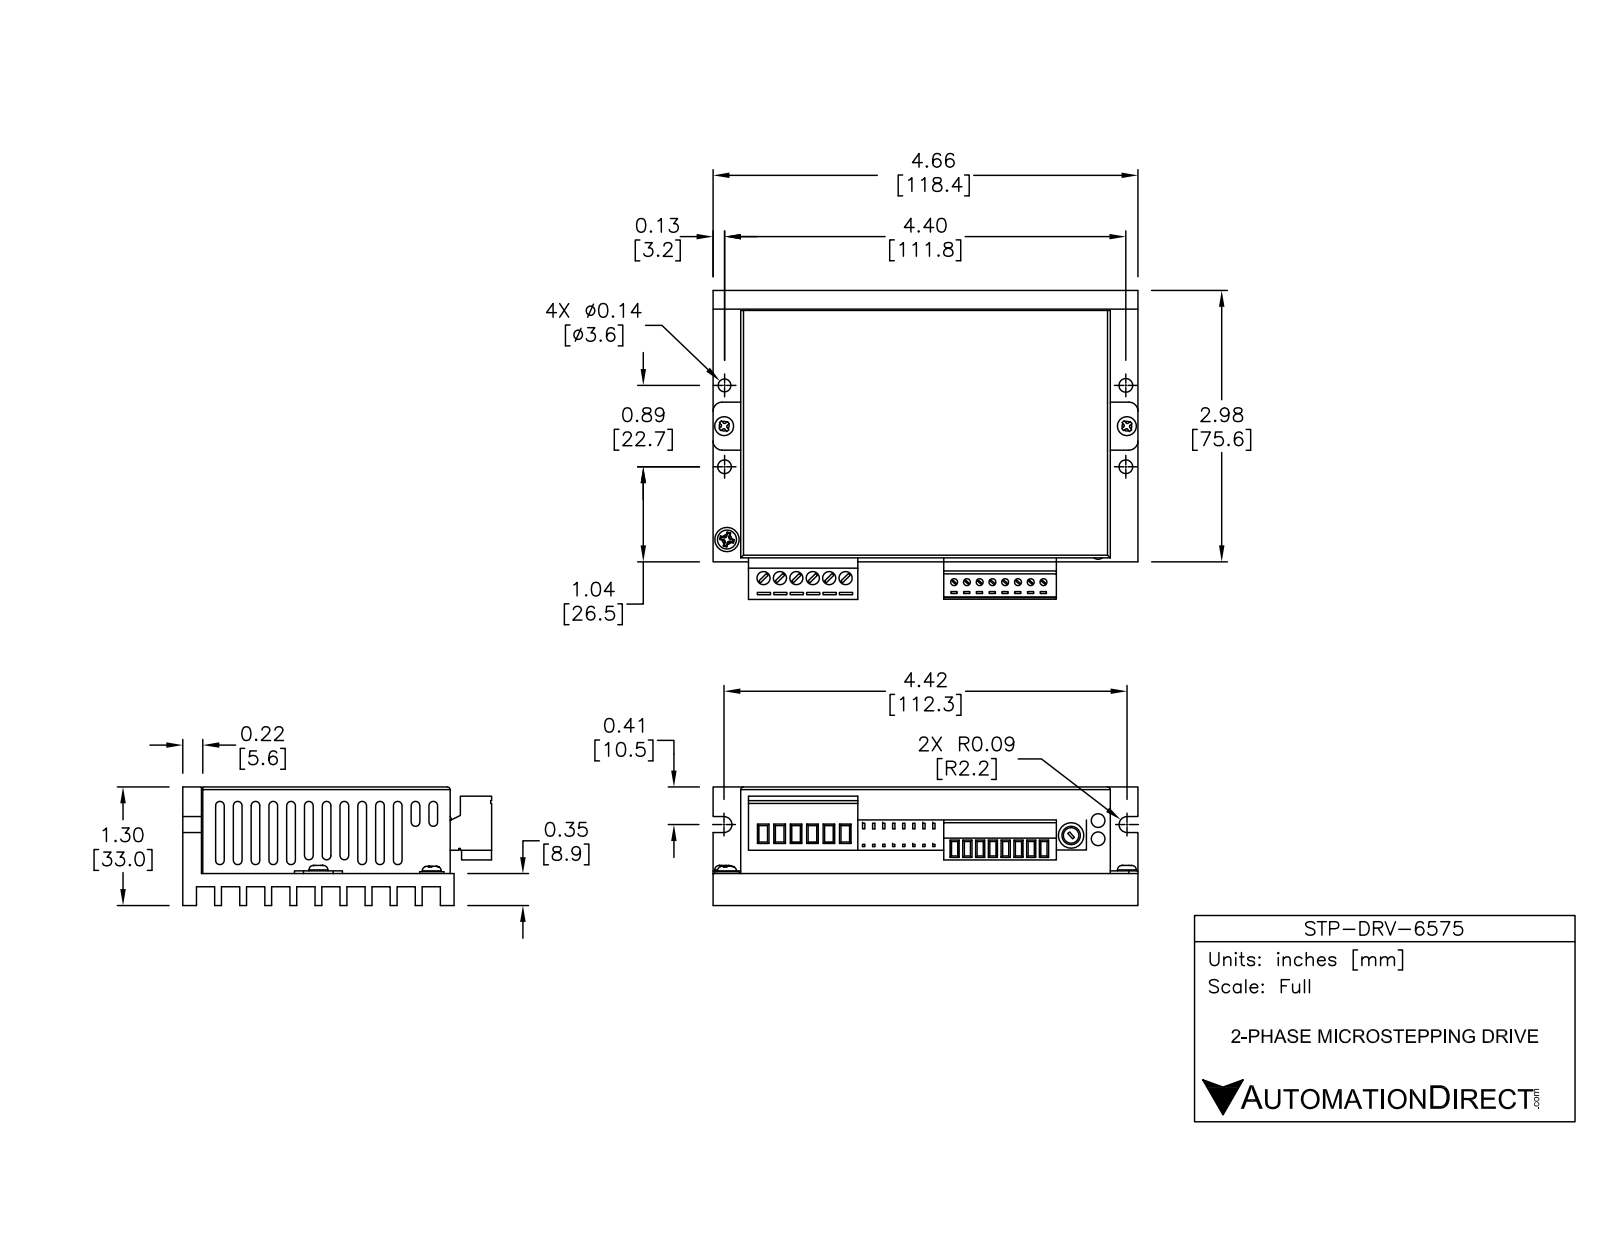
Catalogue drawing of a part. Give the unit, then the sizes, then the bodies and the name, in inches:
Units: inches
Overall size (bounding box): 4.66 × 3.387 × 1.3
Round holes (diameter × count): ⌀0.076 ×8, ⌀0.144 ×6, ⌀0.15 ×6, ⌀0.202 ×1
Round bosses / shafts (diameter × count): ⌀0.207 ×2, ⌀0.278 ×1, ⌀0.266 ×1, ⌀0.208 ×1, ⌀0.17 ×1
Partial cylindrical surfaces — rounded edges, fillets, slot ends (radius × count): R0.048 ×13, R0.048 ×13, R0.046 ×10, R0.015 ×8, R0.1 ×4, R0.03 ×3, R0.087 ×2
Main face-to-face distances: 0.195, 0.1, 0.585, 1.365, 0.095, 0.39, 1.17, 0.29, 0.485, 1.094
Hole centre spacings: 0.28, 0.14, 0.18, 0.42, 0.14, 0.7, 0.36, 0.36
Volume: 11.36 in³ · Surface area: 156 in²
Bodies: 1 solid, 637 faces (515 planar, 109 cylindrical, 13 other)
Part name (STEP PRODUCT): STP-DRV-6575
STEP written by: SolidWorks 2017 (AUTOMOTIVE_DESIGN)
